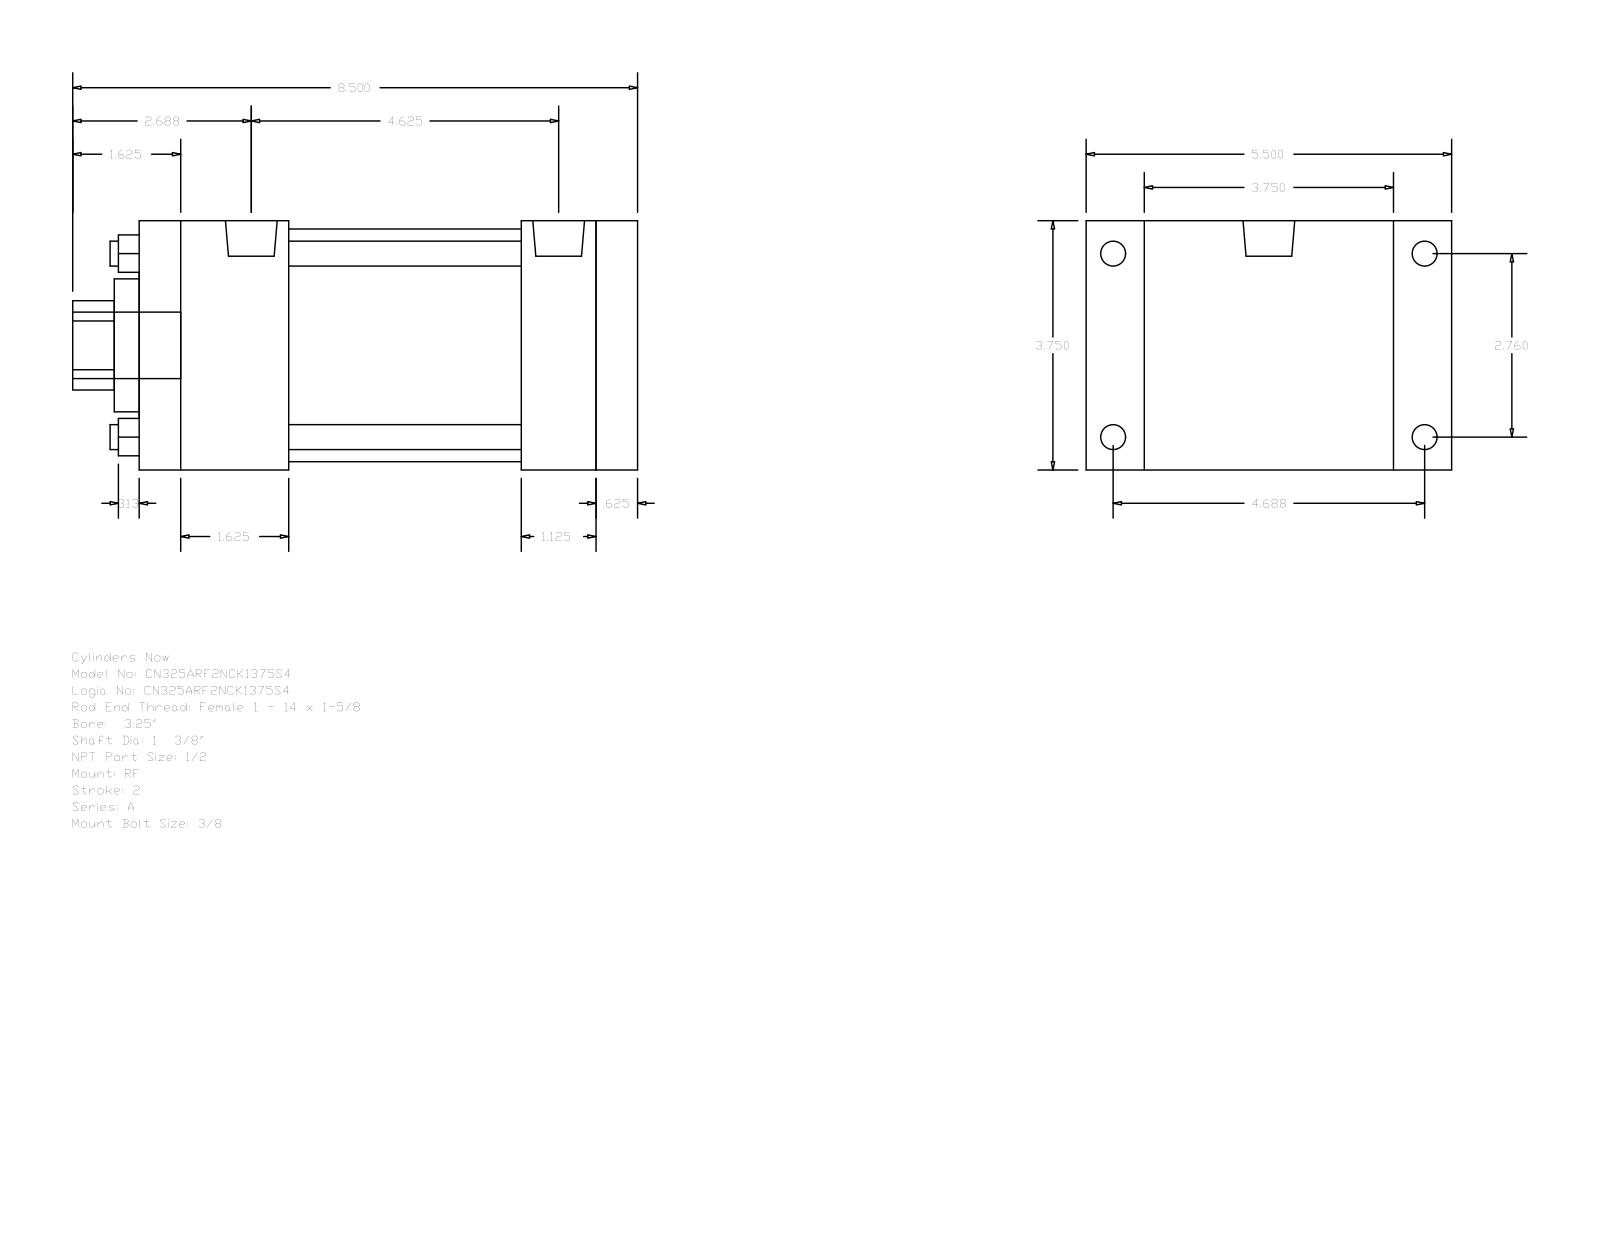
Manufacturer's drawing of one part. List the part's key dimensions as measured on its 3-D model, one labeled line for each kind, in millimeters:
Part name (STEP PRODUCT): A_RF__0325_1.375
STEP written by: GSSL Pune (CONFIG_CONTROL_DESIGN)
Units: millimetres
Bodies: 0 solids, 92 faces (64 planar, 28 cylindrical, 0 other)
Overall size (bounding box): 215.9 × 139.7 × 95.25
Round holes (diameter × count): ⌀9.53 ×4, ⌀34.92 ×1, ⌀50.8 ×1, ⌀88.9 ×1
Round bosses / shafts (diameter × count): ⌀9.53 ×4, ⌀8.73 ×4, ⌀19.77 ×2, ⌀25.4 ×1
Partial cylindrical surfaces — rounded edges, fillets, slot ends (radius × count): R17.06 ×1
Main face-to-face distances: 95.24, 190.5, 15.87, 174.63, 28.58, 22.23, 117.47, 146.05, 44.45, 57.15
Hole centre spacings: 49.57, 70.1, 99.14
